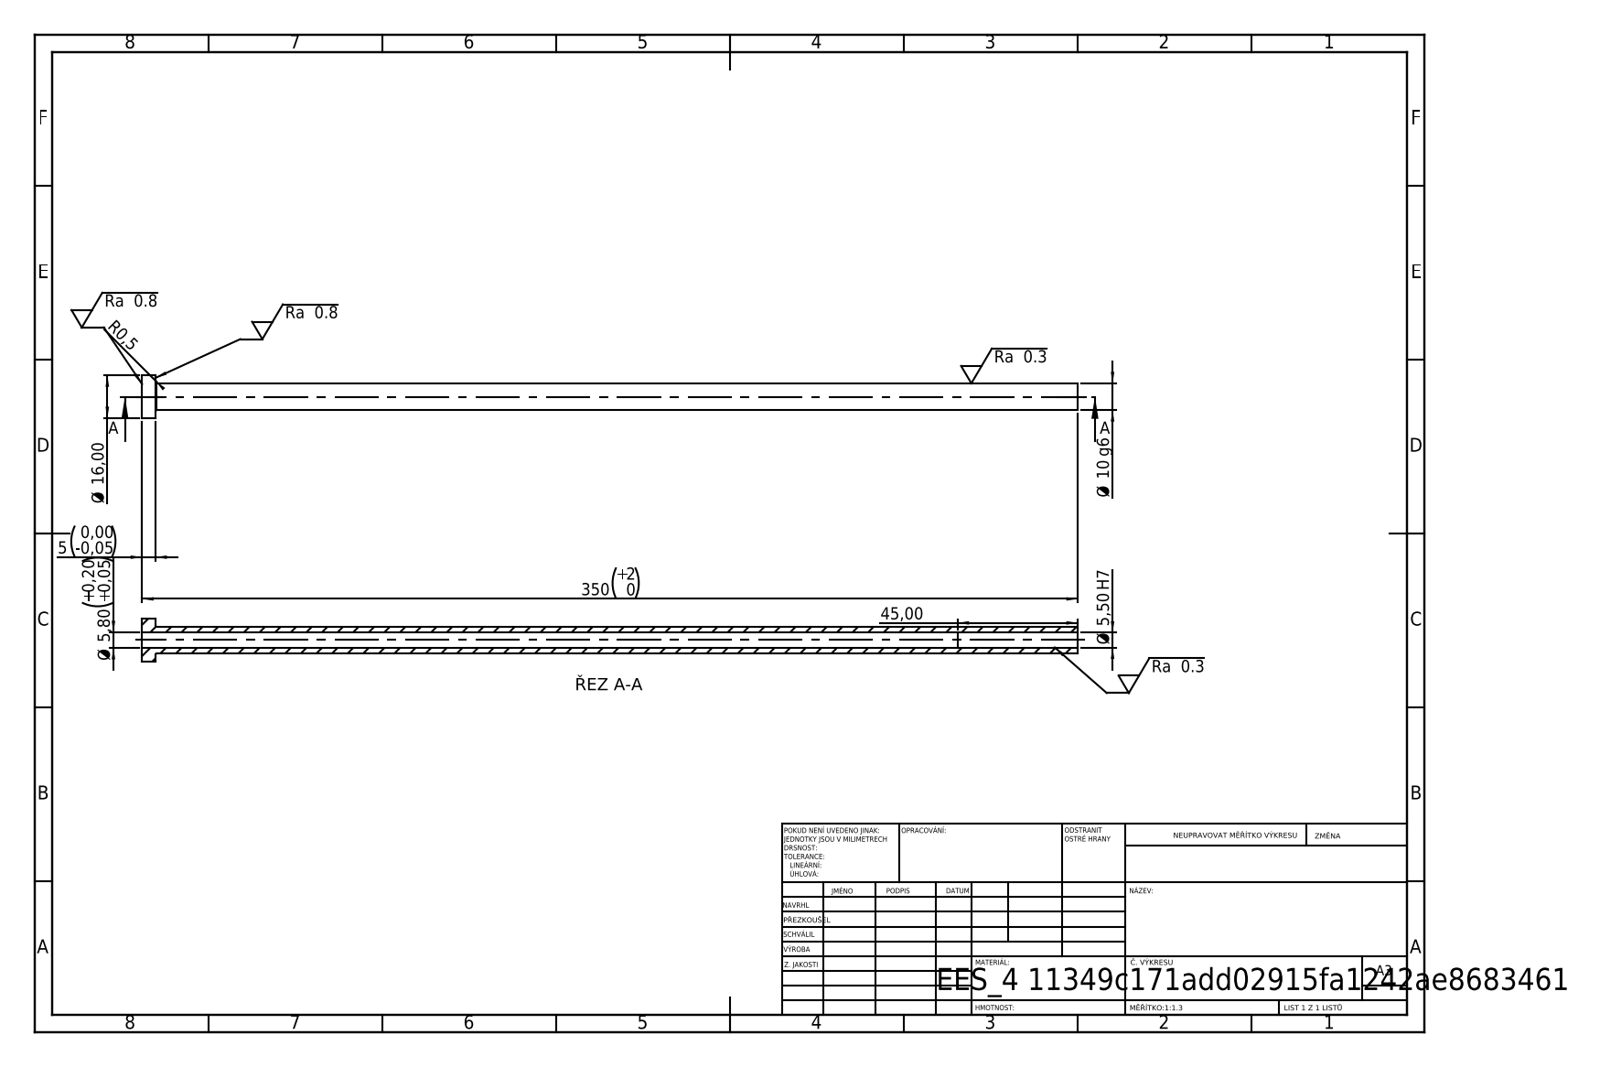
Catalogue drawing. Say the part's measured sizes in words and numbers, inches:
Its 3-D file was written by "SolidWorks 2019 (CONFIG_CONTROL_DESIGN)". It is 1 solid with 14 faces: 4 planar, 8 cylindrical and 2 other. Overall it measures 13.78 by 0.63 by 0.63 inches. Its volume is 1.158 cubic inches and its surface area 27.55 square inches. Round holes: 1 of diameter 0.217, 1 of diameter 0.228. Round bosses or shafts: 1 of diameter 0.63, 1 of diameter 0.394. The main face-to-face distances are 0.197, 13.78, 13.583, 12.008, 11.811, 1.772.
